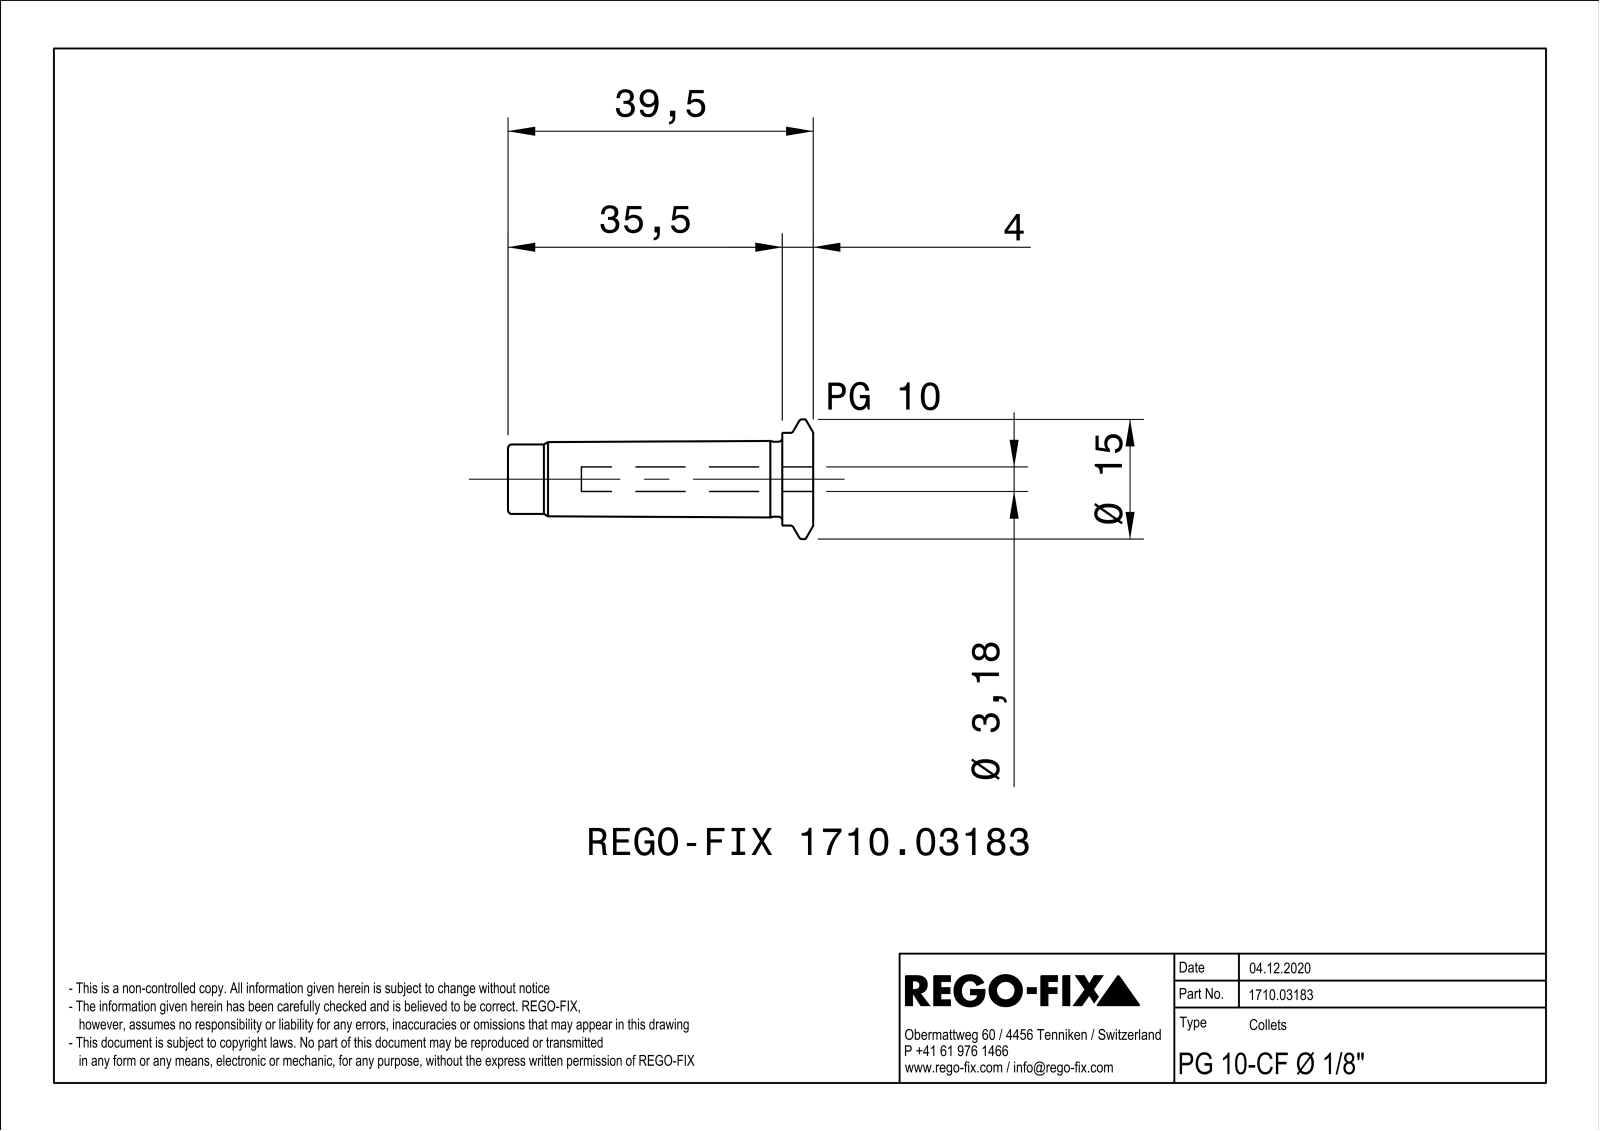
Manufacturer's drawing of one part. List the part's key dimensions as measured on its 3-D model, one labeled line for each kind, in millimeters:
Part name (STEP PRODUCT): NOCUT
STEP written by: SIEMENS PLM Software Solid Edge ST10 (AUTOMOTIVE_DESIGN)
Units: millimetres
Bodies: 0 solids, 68 faces (17 planar, 17 cylindrical, 34 other)
Overall size (bounding box): 39.5 × 15.5 × 15.49
Round holes (diameter × count): ⌀6.19 ×1
Round bosses / shafts (diameter × count): ⌀15.5 ×1, ⌀12 ×1, ⌀9.7 ×1, ⌀9 ×1
Partial cylindrical surfaces — rounded edges, fillets, slot ends (radius × count): R0.5 ×3, R1.59 ×1
Main face-to-face distances: 0.8, 39.5, 4, 35.5
